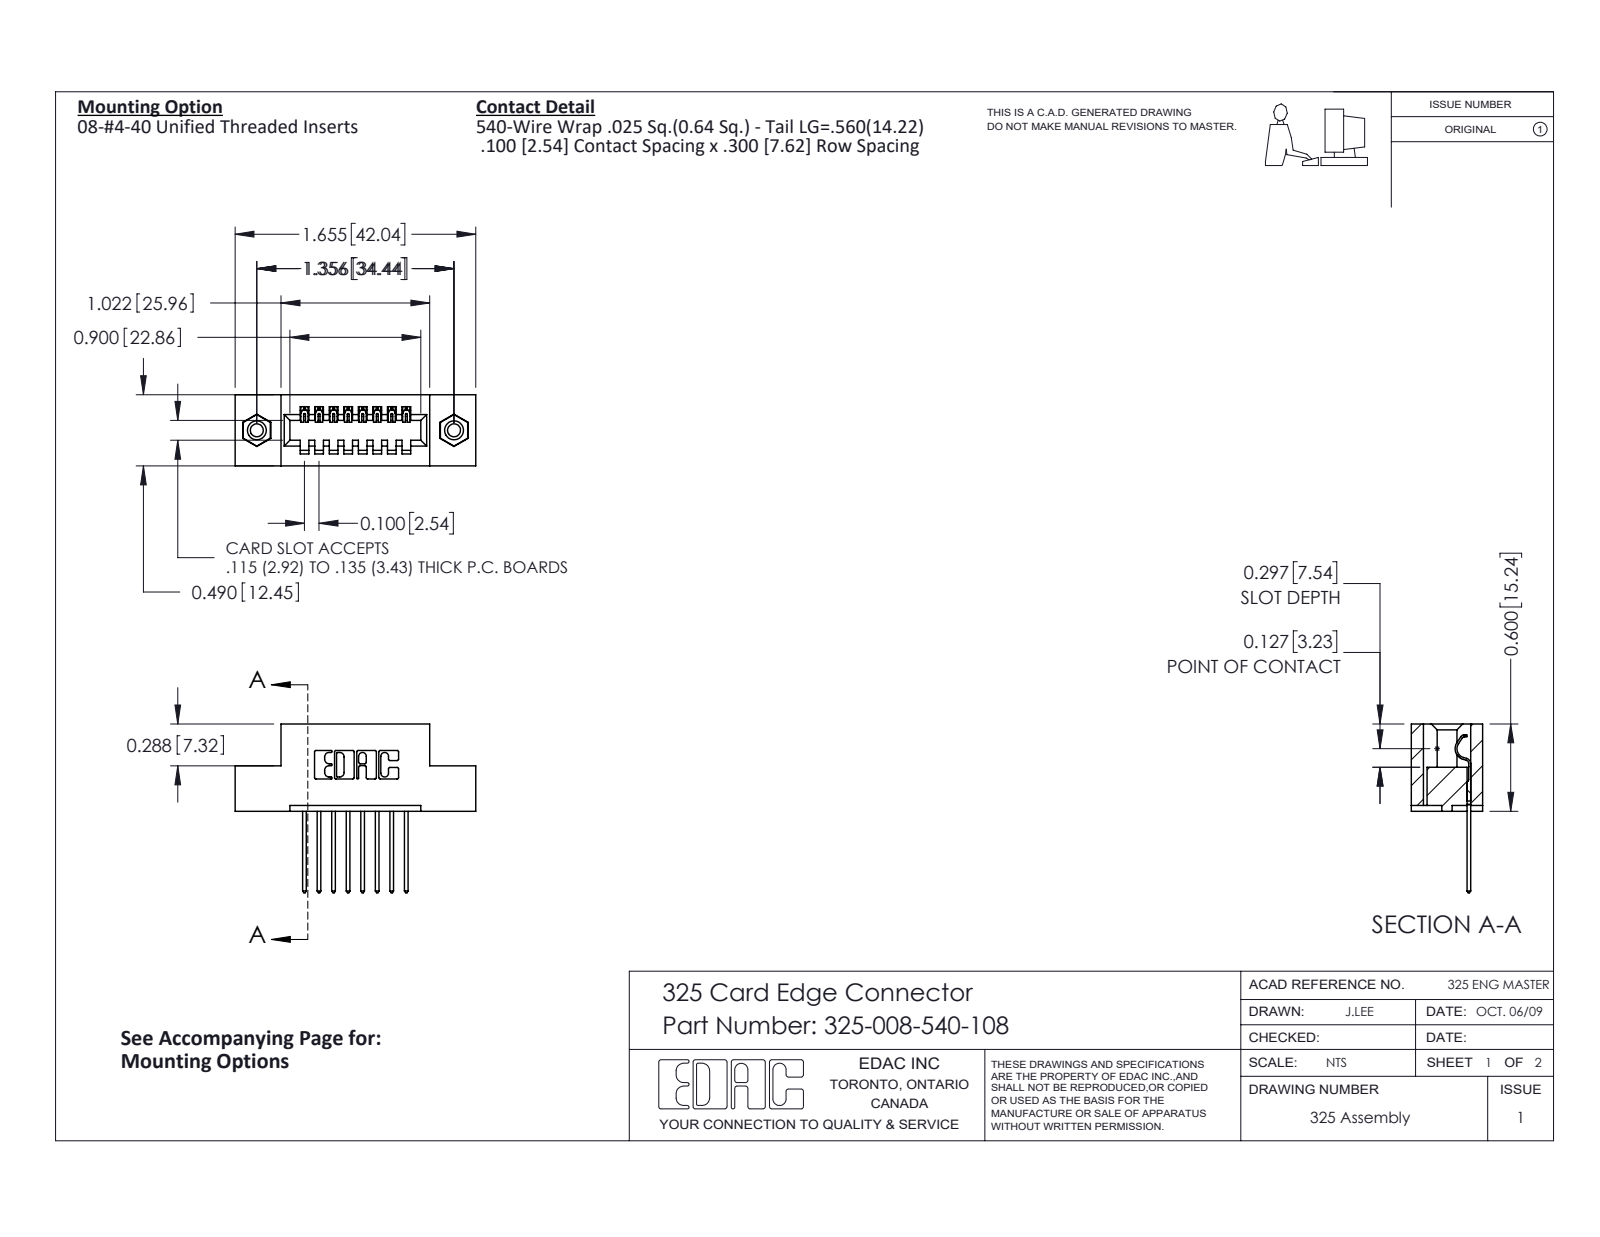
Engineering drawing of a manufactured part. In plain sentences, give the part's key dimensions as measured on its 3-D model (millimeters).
The part is named "325-008-540-108; 325 Part_TI; 345-250-001_345-250-003-102; 325-292-001_325-293-140". Its 3-D file was written by "SolidWorks 2016 (CONFIG_CONTROL_DESIGN)". It is 11 solids with 638 faces: 438 planar, 184 cylindrical and 16 other. Overall it measures 42 by 29.5 by 12.4 millimeters. Its volume is 5 080 cubic millimeters and its surface area 5 062 square millimeters. Round holes: 2 of diameter 2.3, 2 of diameter 3.2, 2 of diameter 4.1. Round bosses or shafts: 2 of diameter 3.9. Partial cylindrical surfaces (rounded edges, fillets, slot ends): 22 of radius 0.3, 16 of radius 0.2, 16 of radius 0.3, 6 of radius 0.2, 6 of radius 0.8, 3 of radius 0.7, 1 of radius 0.4, 1 of radius 0.6. The main face-to-face distances are 7.6, 2.5, 5.1, 1, 2.1, 10.3, 12.4, 10.2, 1.5, 15.2. The hole center spacings are 34.4.
